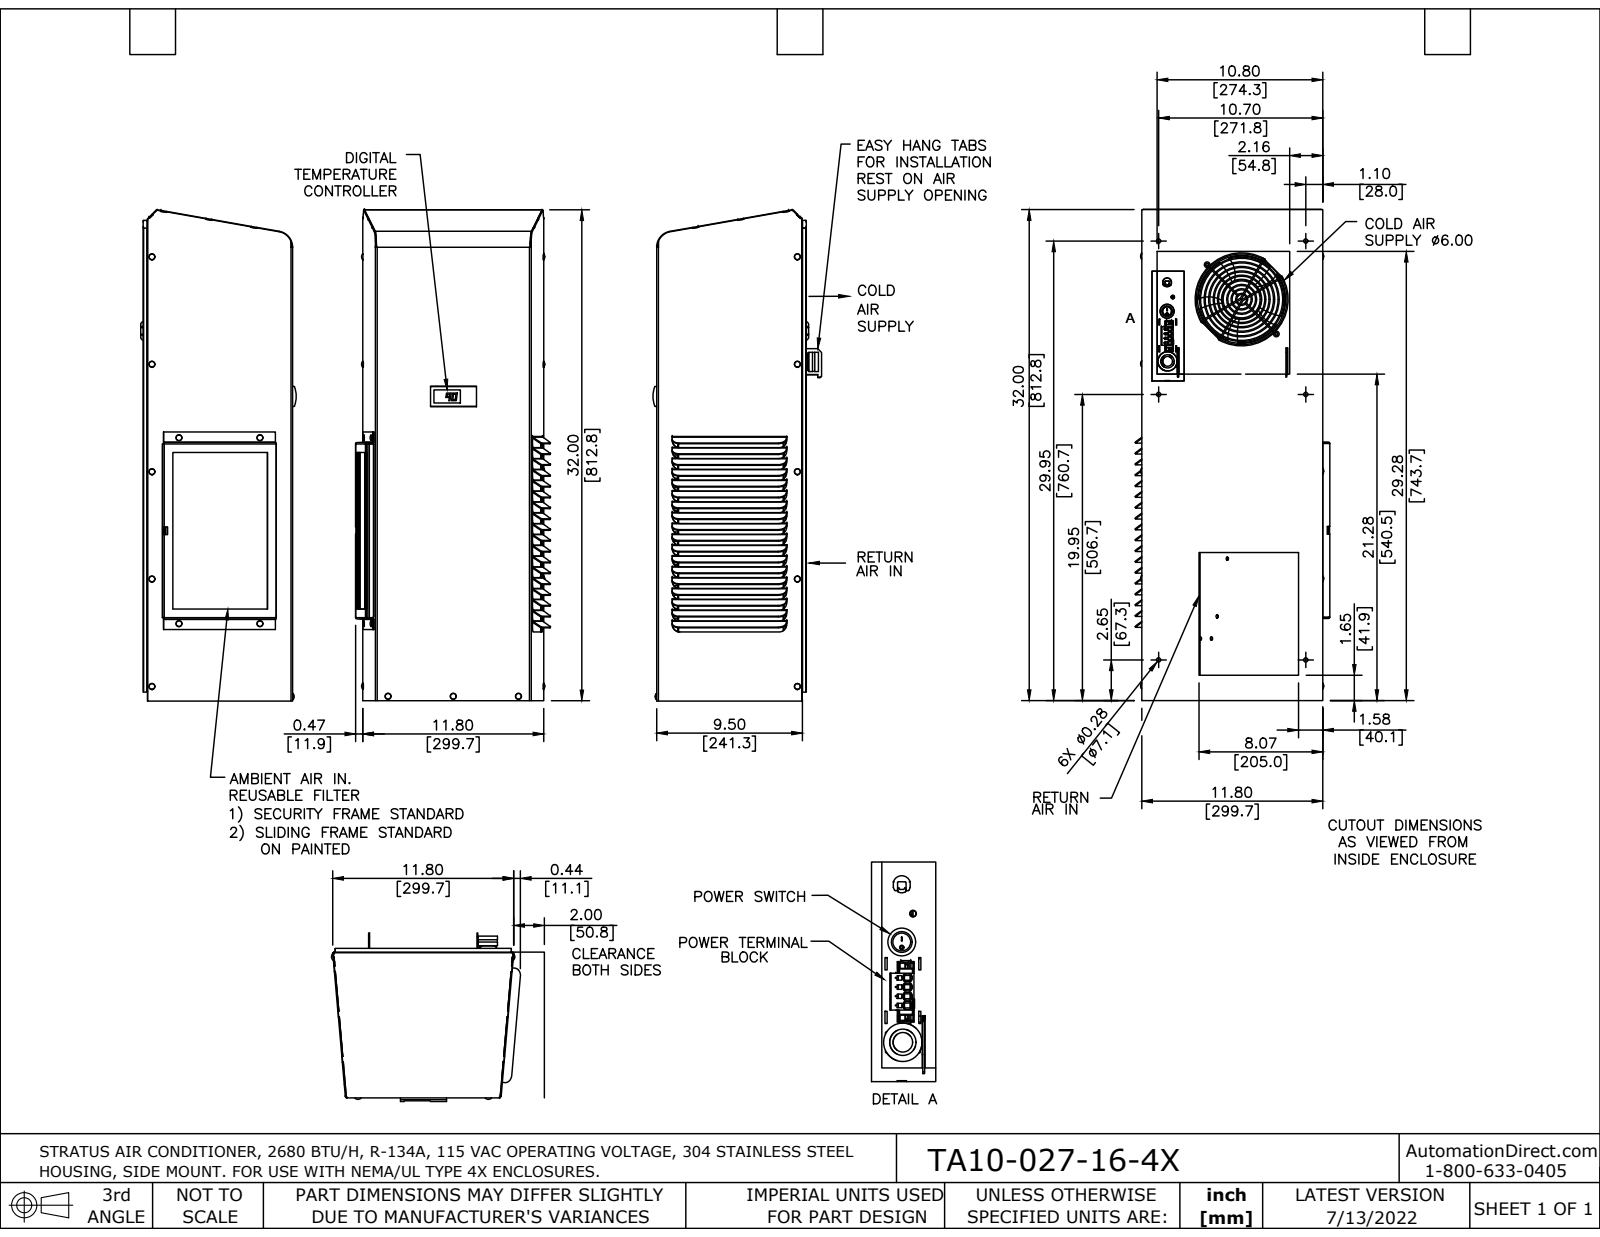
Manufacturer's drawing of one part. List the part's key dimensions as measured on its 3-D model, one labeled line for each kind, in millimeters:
Part name (STEP PRODUCT): TA10-027-16-4X
STEP written by: SolidWorks 2021 (AUTOMOTIVE_DESIGN)
Units: millimetres
Bodies: 1 solid, 1571 faces (959 planar, 469 cylindrical, 143 other)
Overall size (bounding box): 813.4 × 319.4 × 293.3
Volume: 2 361 000 mm³ · Surface area: 2 057 000 mm²
Round holes (diameter × count): ⌀4 ×11, ⌀6.2 ×10, ⌀5.2 ×3, ⌀152.4 ×1
Round bosses / shafts (diameter × count): ⌀12.7 ×10, ⌀4.8 ×7, ⌀6.3 ×2, ⌀154.2 ×1, ⌀23 ×1, ⌀2.2 ×1
Partial cylindrical surfaces — rounded edges, fillets, slot ends (radius × count): R0.4 ×45, R0.3 ×42, R12.7 ×36, R12.9 ×36, R2.5 ×28, R1.5 ×21, R2.9 ×21, R0.8 ×12
Main face-to-face distances: 1.5, 239.6, 238.2, 241.1, 1.5, 8.8, 10.3, 1.5, 6.4, 7.8
Hole centre spacings: 129.9, 177.8, 355.6, 103.9, 533.4, 33.9, 129.9, 17.6
